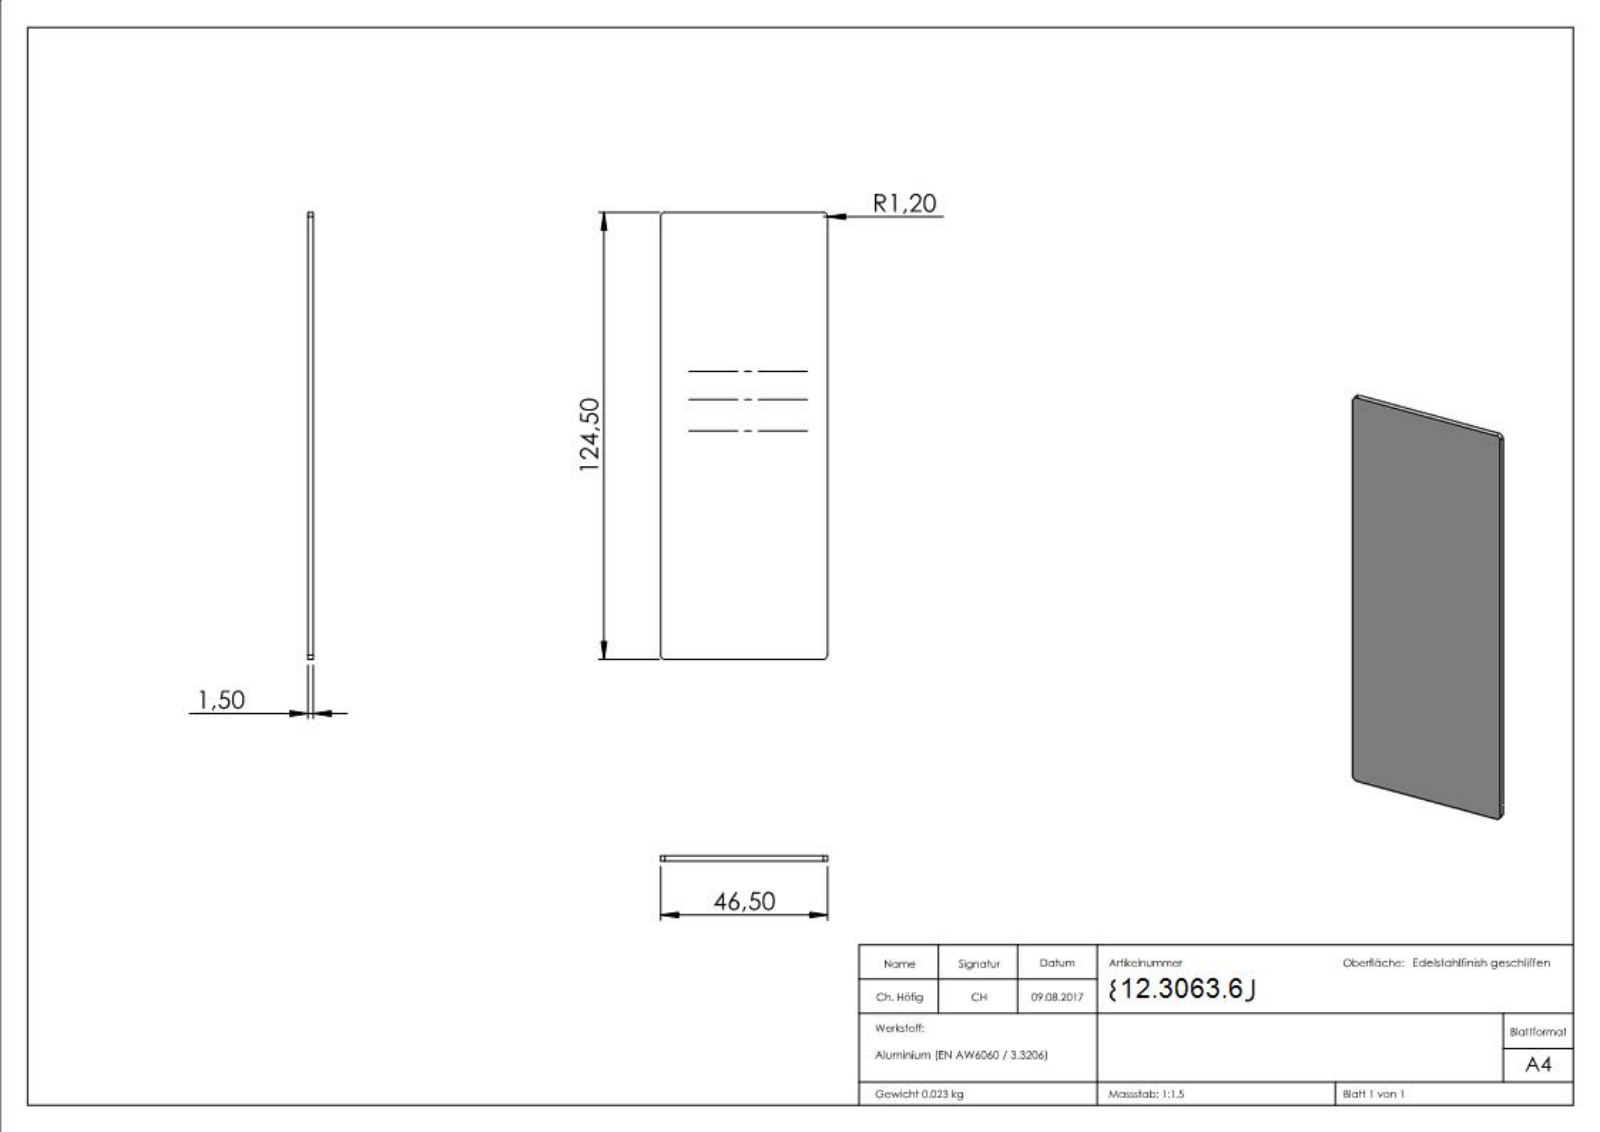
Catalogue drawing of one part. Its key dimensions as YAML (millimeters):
part_name: "80552-ALU"
step_written_by: "SolidWorks 2015 (CONFIG_CONTROL_DESIGN)"
units: millimeters
bodies: {solids: 1, faces: 236, planar: 129, cylindrical: 4, other: 103}
overall_size: [124.5, 46.5, 1.5]
volume: 8681
surface_area: 12096
partial_cylinders:
  - {radius: 1.2, count: 4}
face_to_face_distances: [1.5, 46.5, 124.5, 1.4, 1.32, 3.2, 3.71, 1.19, 3.66, 6.98]
